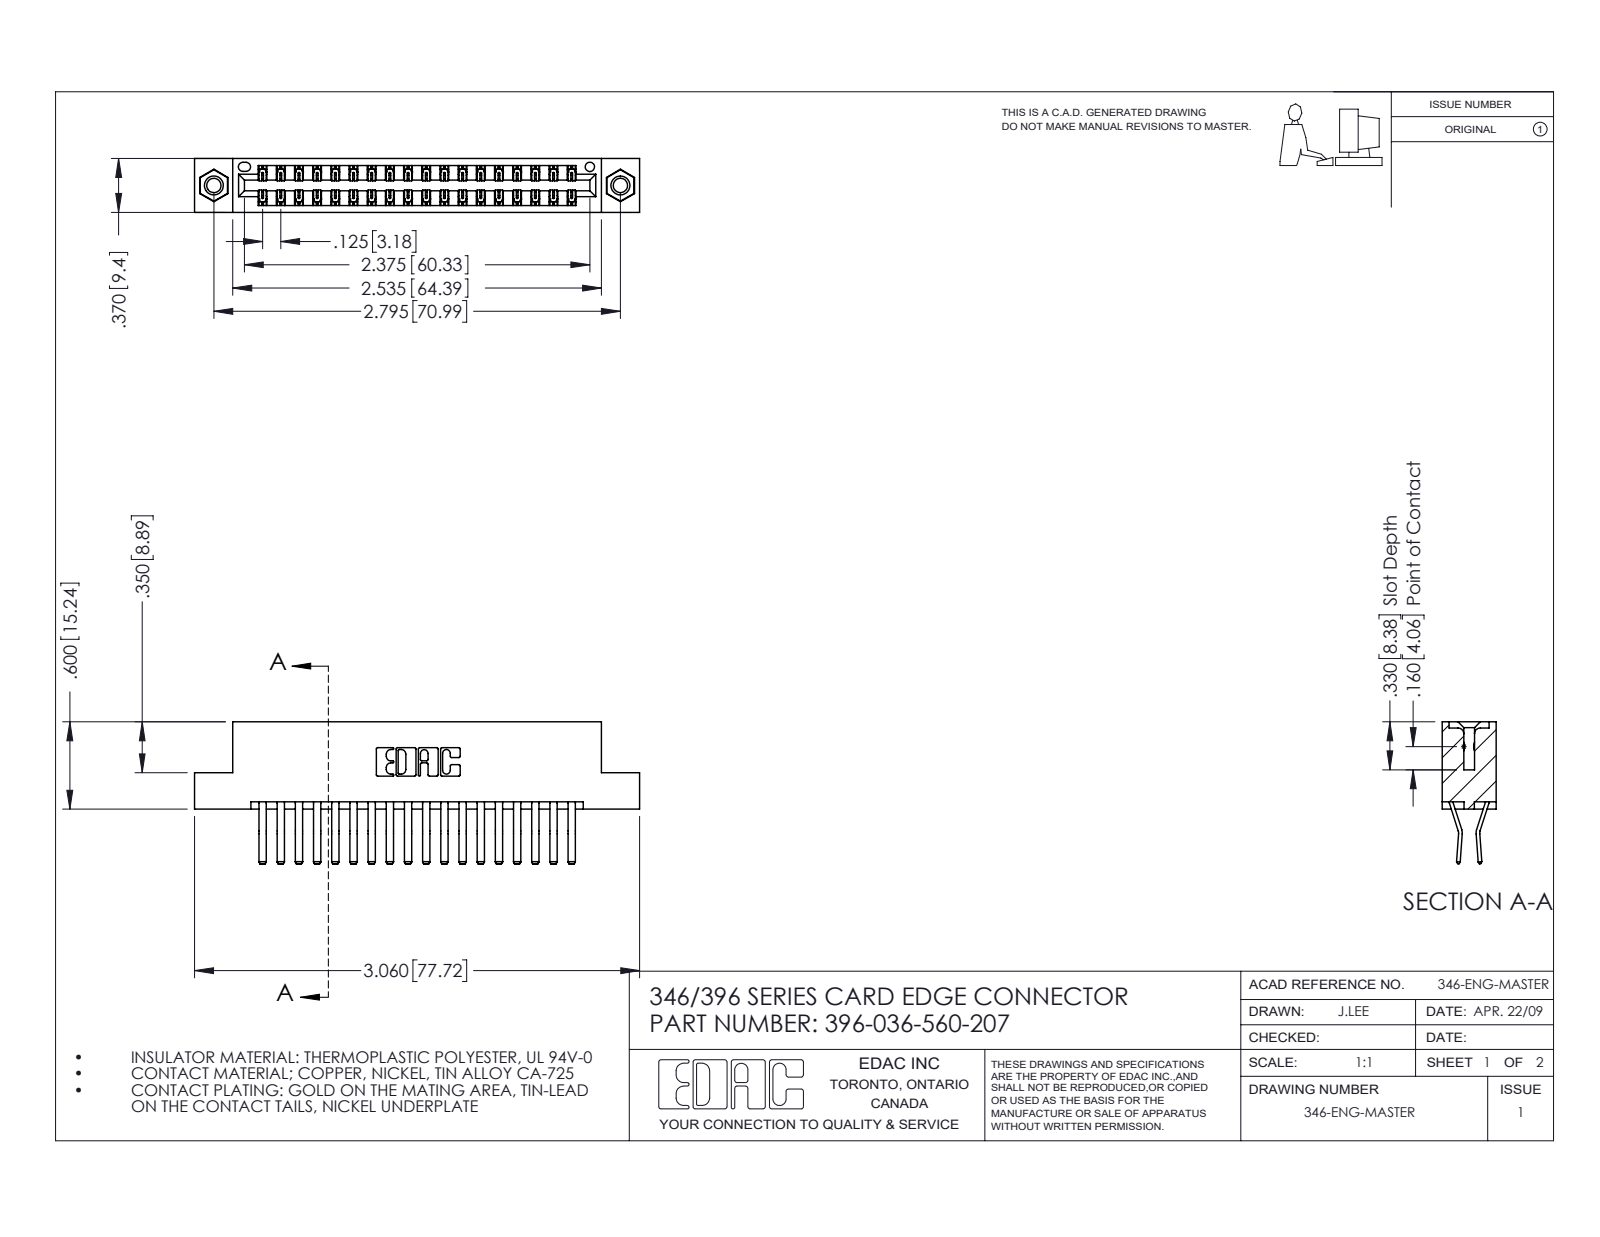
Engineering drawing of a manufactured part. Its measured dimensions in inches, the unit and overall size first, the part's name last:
Units: inches
Overall size (bounding box): 3.06 × 0.975 × 0.37
Round holes (diameter × count): ⌀0.098 ×2, ⌀0.125 ×2, ⌀0.156 ×2, ⌀0.064 ×1
Round bosses / shafts (diameter × count): ⌀0.155 ×2
Partial cylindrical surfaces — rounded edges, fillets, slot ends (radius × count): R0.006 ×54, R0.01 ×22, R0.007 ×6, R0.031 ×6, R0.026 ×3, R0.01 ×2, R0.014 ×2, R0.022 ×2
Main face-to-face distances: 0.048, 0.322, 0.25, 0.37, 0.025, 0.072, 0.298, 0.275, 0.148, 0.222
Hole centre spacings: 0.246, 2.588, 2.795
Volume: 0.465 in³ · Surface area: 16.67 in²
Bodies: 39 solids, 2126 faces (1368 planar, 742 cylindrical, 16 other)
Part name (STEP PRODUCT): 346 Part_Flush Mounting Lugs - 0.156 Dia-TI; 345-250-001_345-250-005-103; 345-292-001_560 Tail; 396-036-560-207
STEP written by: SolidWorks 2016 (CONFIG_CONTROL_DESIGN)
